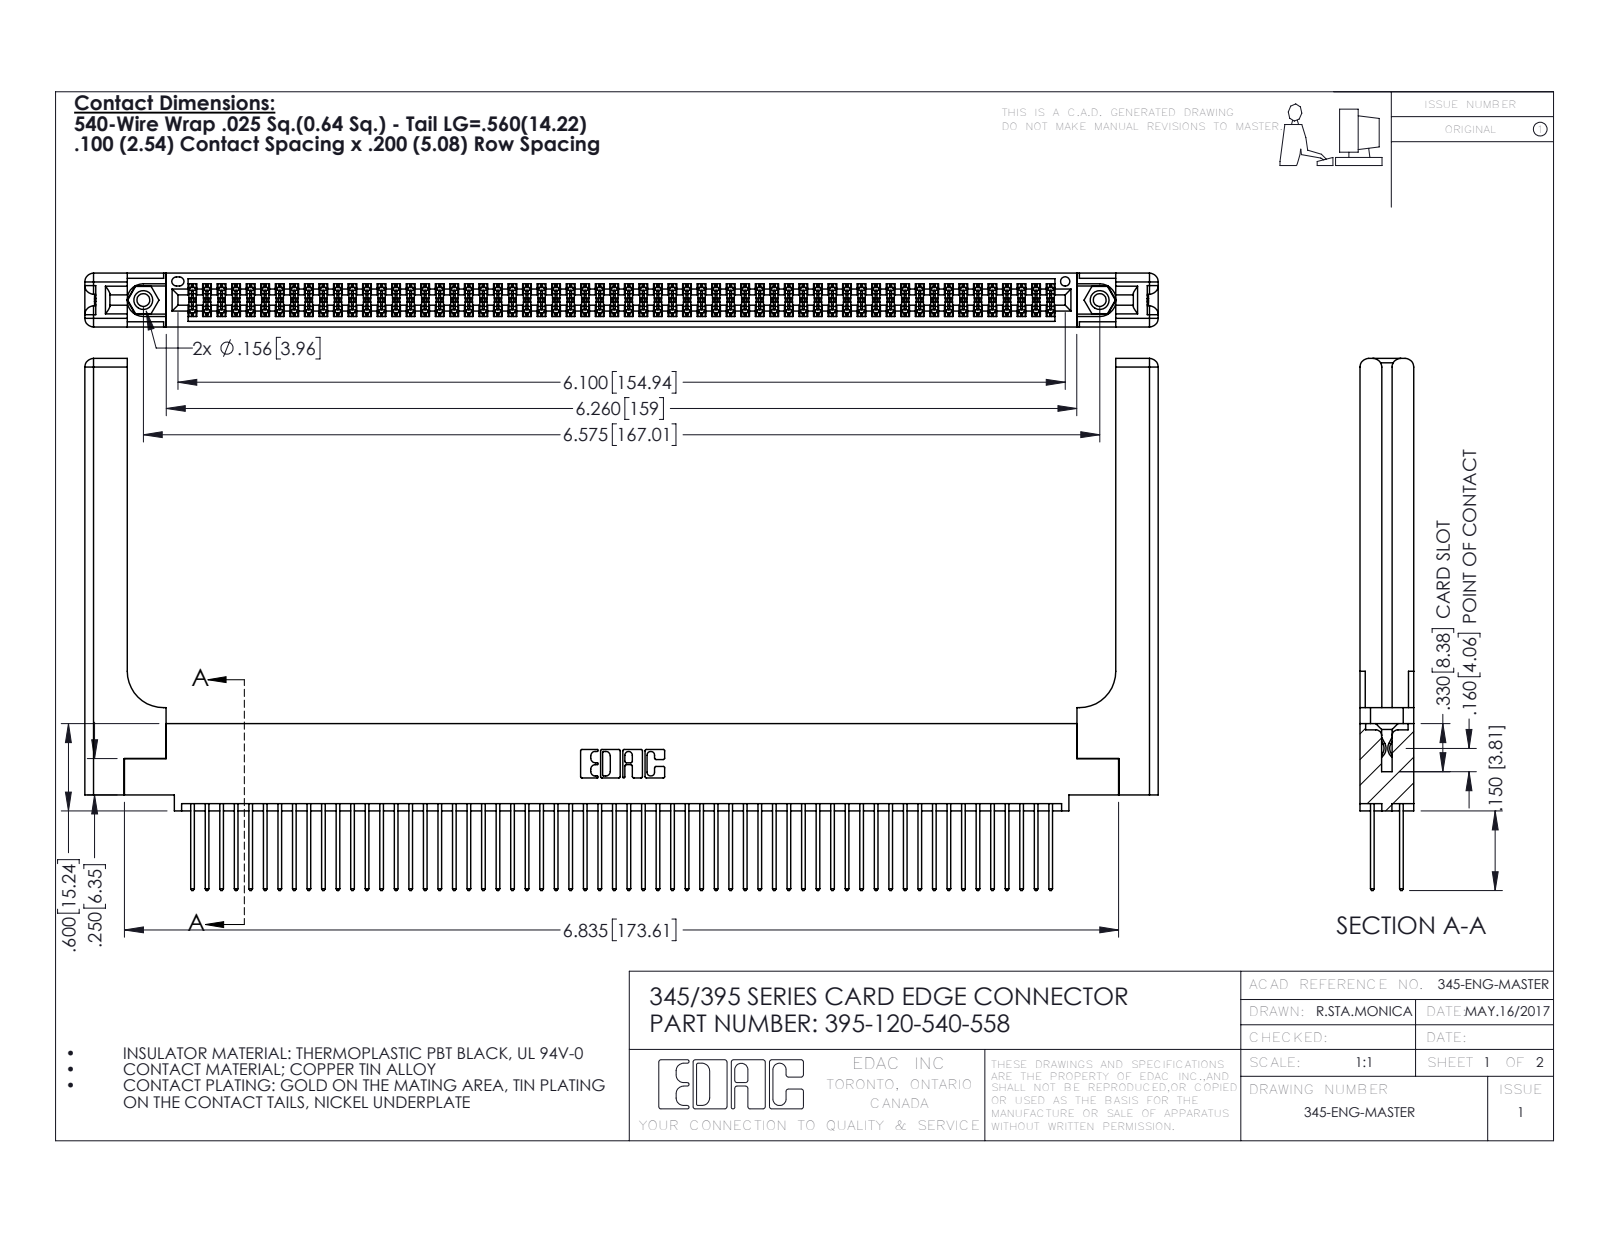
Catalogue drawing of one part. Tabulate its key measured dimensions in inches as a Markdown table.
| quantity | value |
| --- | --- |
| part name | 395-120-540-558; 345 Part_0.110 Offset - 0.156 Dia-TH; 345-220-058_345-220-058; 345-250-001_345-250-001-102 (+1 more) |
| STEP written by | SolidWorks 2016 (CONFIG_CONTROL_DESIGN) |
| units | inches |
| bodies | 125 solids, 6386 faces (4192 planar, 2134 cylindrical, 60 other) |
| overall size | 7.379 × 3.657 × 0.37 |
| volume | 1.662 in³ |
| surface area | 54.77 in² |
| round holes (diameter × count) | 0.089 × 2, 0.125 × 2, 0.156 × 2, 0.064 × 1 |
| round bosses / shafts (diameter × count) | 0.155 × 2 |
| partial cylindrical surfaces (radius × count) | 0.006 × 180, 0.01 × 120, 0.01 × 22, 0.06 × 16, 0.007 × 6, 0.031 × 6, 0.026 × 3, 0.014 × 2 |
| main face-to-face distances | 0.072, 0.298, 0.37, 0.098, 0.272, 0.025, 0.2, 0.225, 0.175, 0.148 |
| hole center spacings | 0.27, 6.339, 6.575 |
